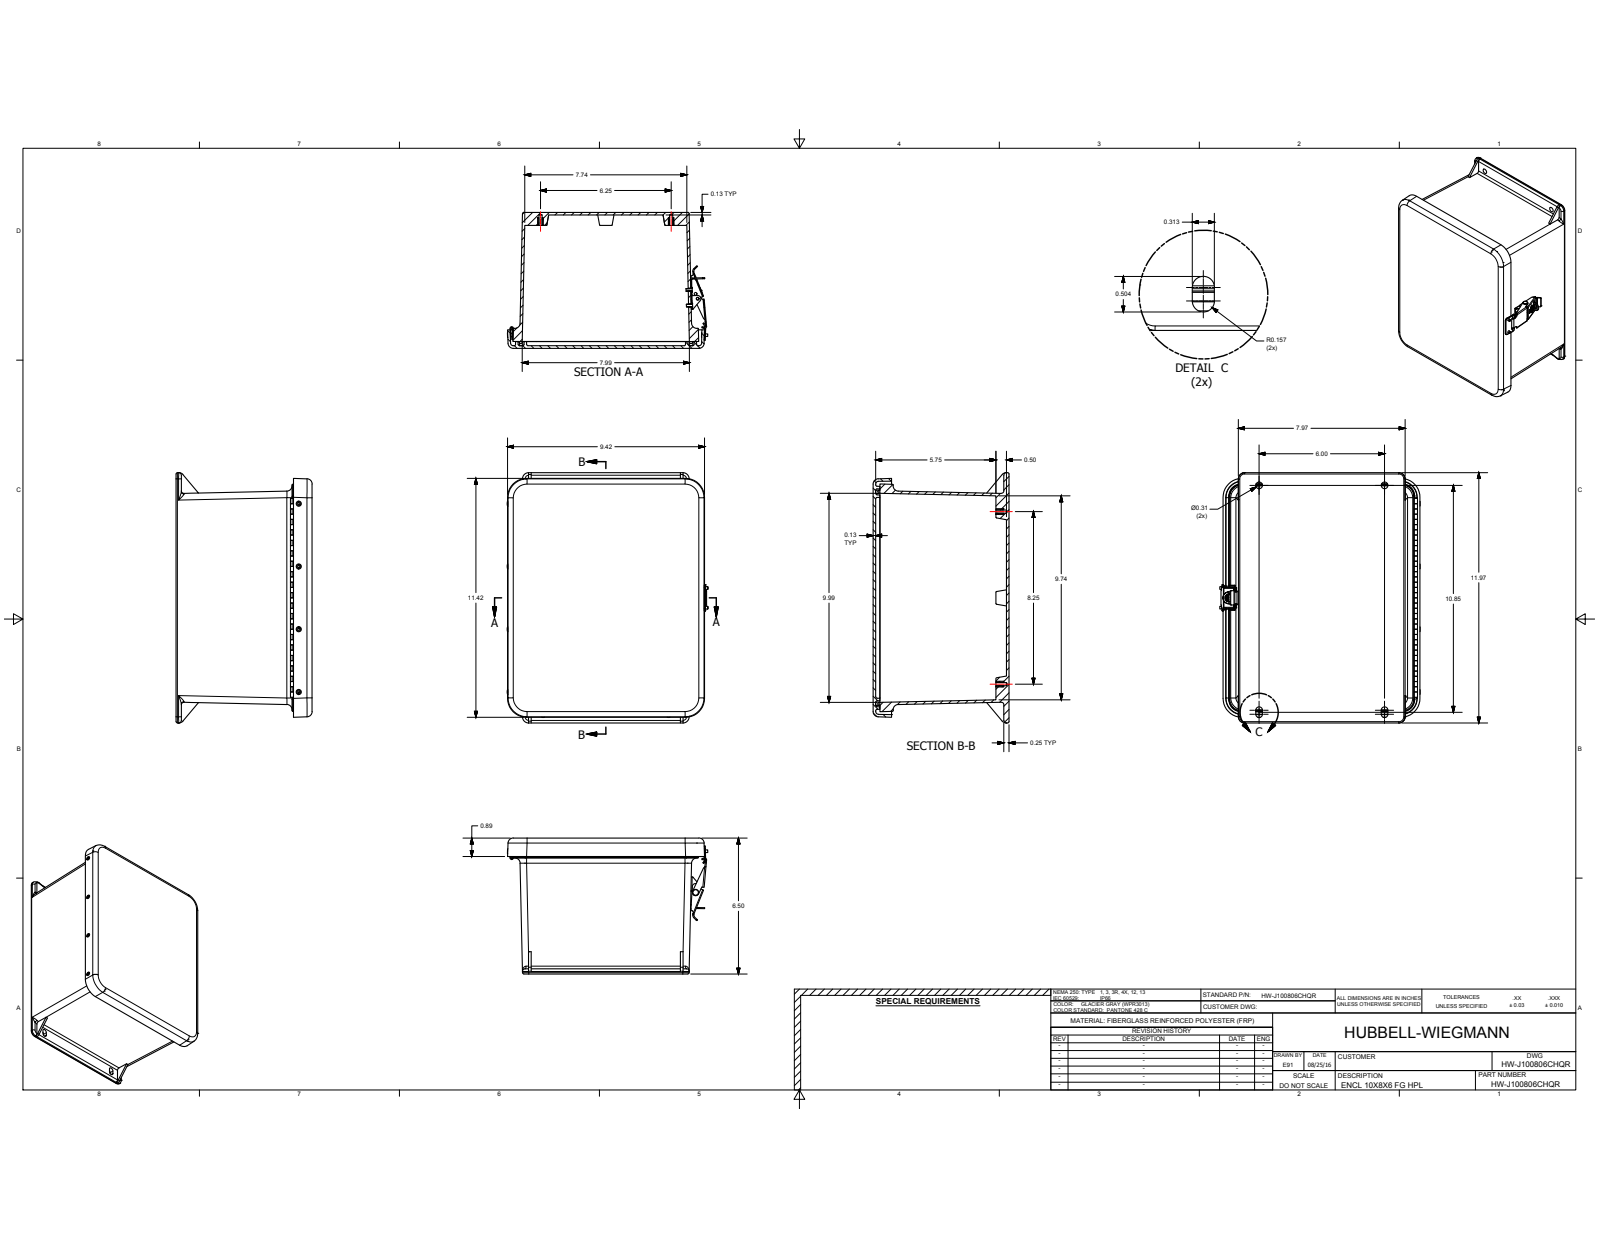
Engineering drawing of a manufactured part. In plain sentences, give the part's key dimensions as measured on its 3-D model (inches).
The part is named "J100806HPL_STP; WPJ100806H&LBOX; WPJ100806HLU; WPJ100806H&LCVR (+8 more)". Its 3-D file was written by "Autodesk Inventor 2017 (AUTOMOTIVE_DESIGN)". It is 36 solids with 1172 faces: 450 planar, 454 cylindrical and 268 other. Overall it measures 11.966 by 9.846 by 6.499 inches. Its volume is 76.58 cubic inches and its surface area 1 030 square inches. Round holes: 14 of diameter 0.14, 12 of diameter 0.104, 12 of diameter 0.152, 12 of diameter 0.159, 8 of diameter 0.131, 5 of diameter 0.375, 2 of diameter 0.13, 2 of diameter 0.135, 2 of diameter 0.313, 1 of diameter 0.085. Round bosses or shafts: 12 of diameter 0.27, 12 of diameter 0.125, 1 of diameter 0.3, 1 of diameter 0.17, 1 of diameter 0.155, 1 of diameter 0.12. Partial cylindrical surfaces (rounded edges, fillets, slot ends): 33 of radius 0.063, 26 of radius 0.031, 22 of radius 0.125, 20 of radius 0.063, 16 of radius 0.039, 12 of radius 0.015, 12 of radius 0.3, 10 of radius 0.25. The main face-to-face distances are 0.125, 6.499, 0.122, 0.123, 6.374, 6.249, 0.125, 6.374, 6.172, 6.047. The hole center spacings are 6, 3, 2.5, 0.938, 3.5, 8.5, 9, 0.75.
